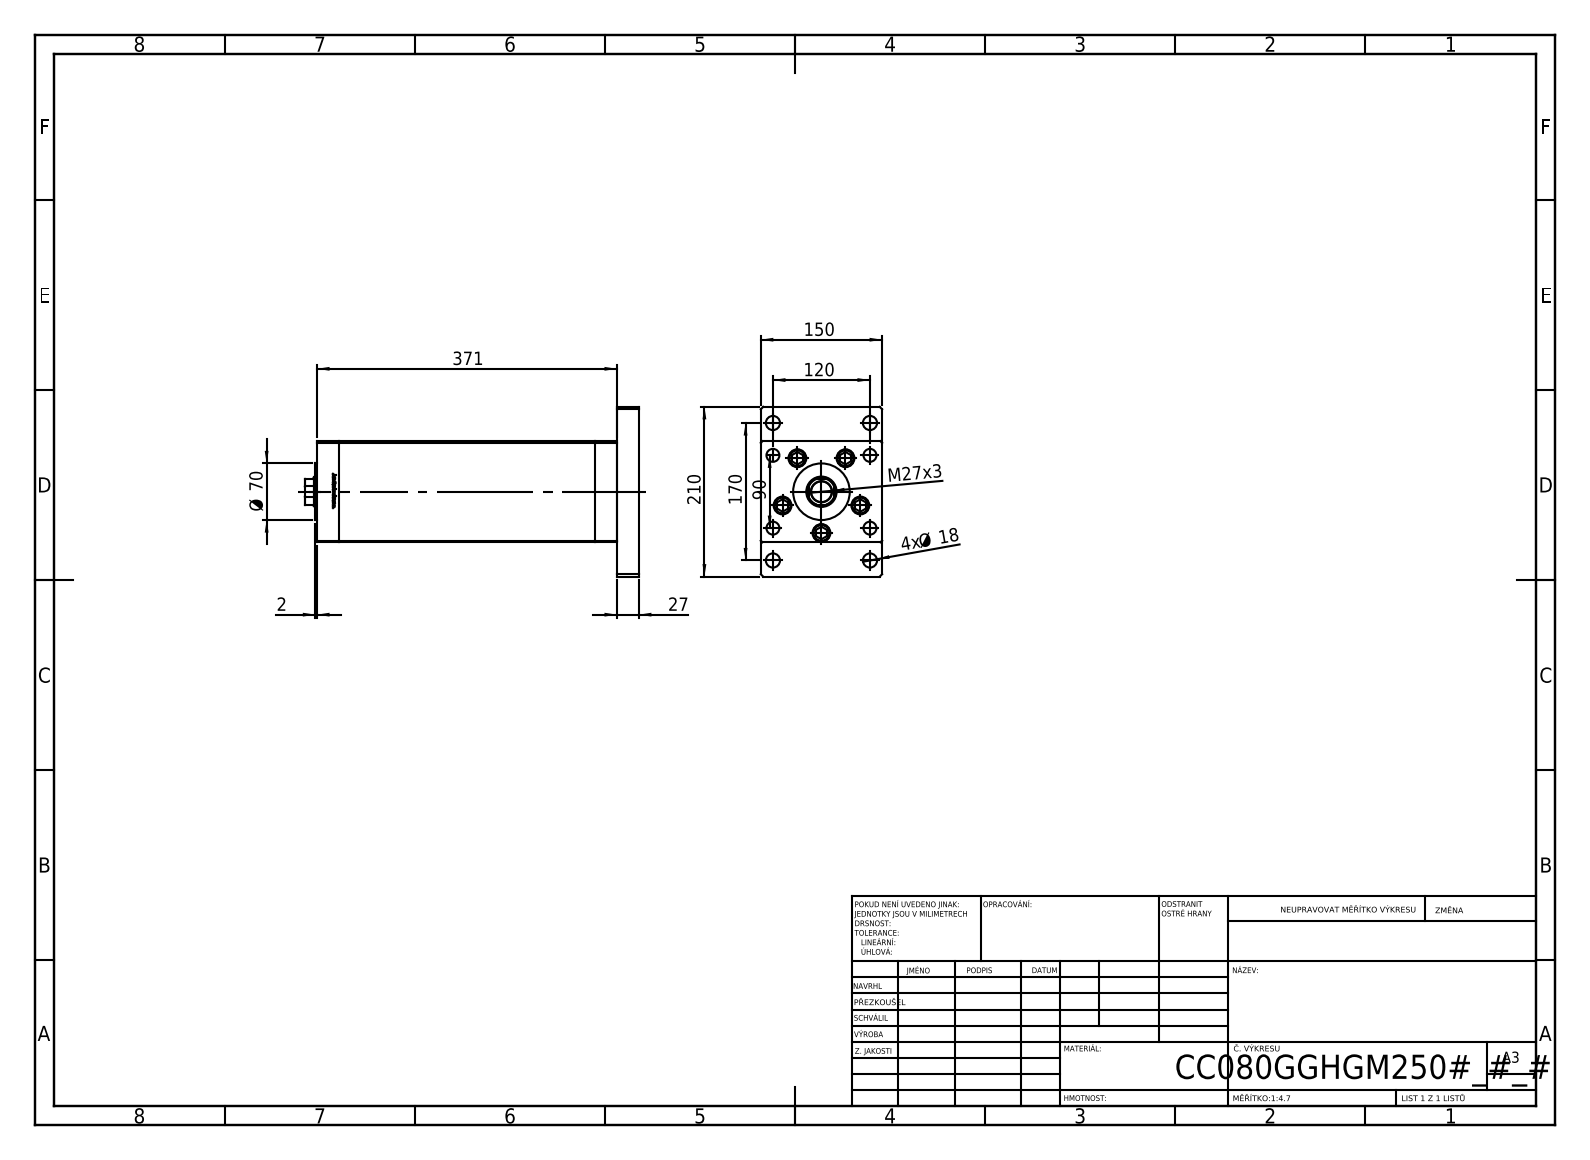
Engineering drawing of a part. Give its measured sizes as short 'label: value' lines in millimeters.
name: V220C_VC_G; V220C_FRONT_G; V220C BACK_G; V220C_G_MIDDLE (+2 more)
written by: SolidWorks 2019 (CONFIG_CONTROL_DESIGN)
unit: mm
bodies: 19 solids, 1313 faces (518 planar, 189 cylindrical, 606 other)
size: 413 × 210 × 150
volume: 6 517 000 mm³; area: 608 121 mm²
holes: 9× ⌀16, 9× ⌀17.5, 5× ⌀22, 4× ⌀21, 2× ⌀2, 2× ⌀13.16, 1× ⌀25.5, 1× ⌀36, 1× ⌀37.5, 1× ⌀102
bosses: 9× ⌀8, 5× ⌀21, 1× ⌀80, 1× ⌀70
rounds: 2× R0.93, 1× R17.5
face distances: 27, 150, 125, 344, 371, 317, 54, 2, 398, 369
hole spacings: 51, 40, 75, 104.04, 120, 126.49, 130, 176.92
